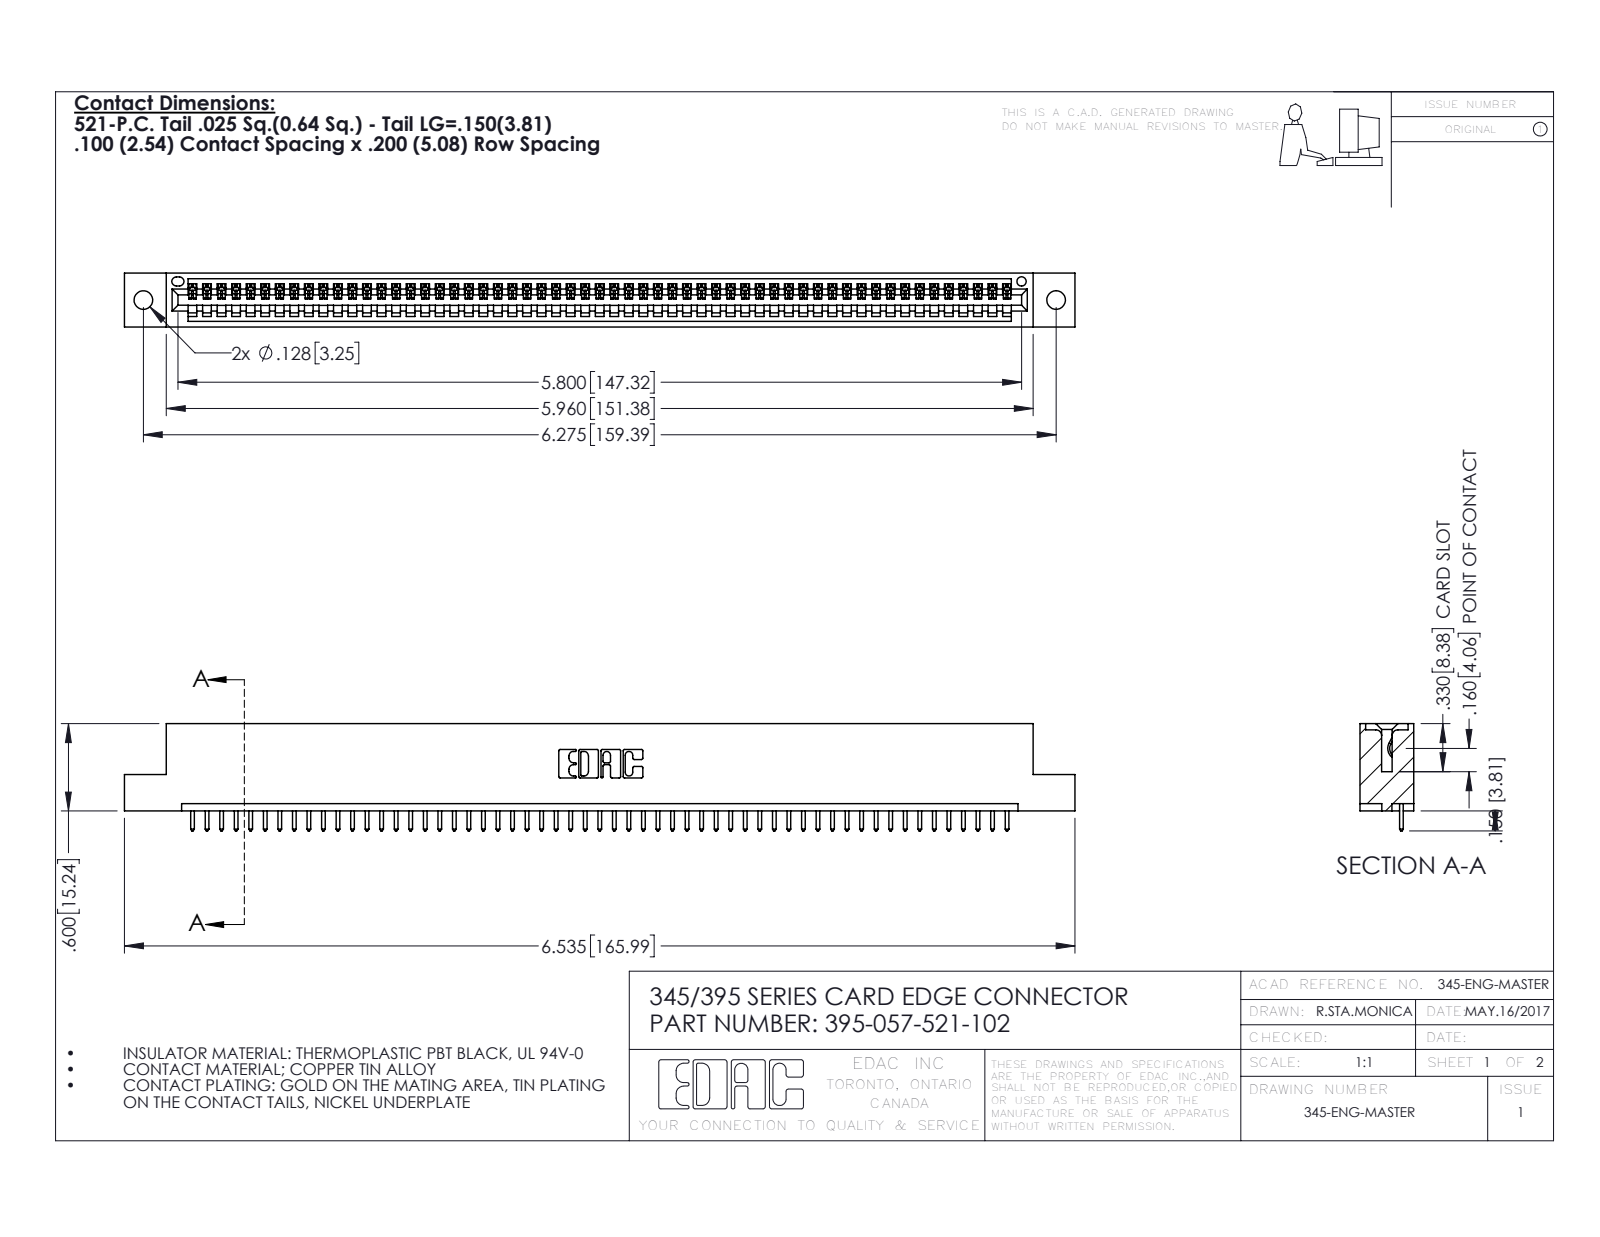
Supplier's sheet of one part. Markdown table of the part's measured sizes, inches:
| quantity | value |
| --- | --- |
| part name | 345-292-001_345-293-121; 395-057-521-102; 345 Part_Flush Mounting Lugs - 0.128 Dia |
| STEP written by | SolidWorks 2016 (CONFIG_CONTROL_DESIGN) |
| units | inches |
| bodies | 58 solids, 3432 faces (2360 planar, 1072 cylindrical, 0 other) |
| overall size | 6.535 × 0.737 × 0.37 |
| volume | 0.957 in³ |
| surface area | 31.23 in² |
| round holes (diameter × count) | 0.128 × 2, 0.064 × 1 |
| partial cylindrical surfaces (radius × count) | 0.006 × 114, 0.01 × 114, 0.01 × 22, 0.007 × 6, 0.031 × 6, 0.026 × 3, 0.031 × 2, 0.04 × 2 |
| main face-to-face distances | 0.298, 0.072, 0.37, 0.2, 0.098, 0.272, 0.025, 0.225, 0.149, 0.072 |
| hole center spacings | 0.27, 6.039, 6.275 |
